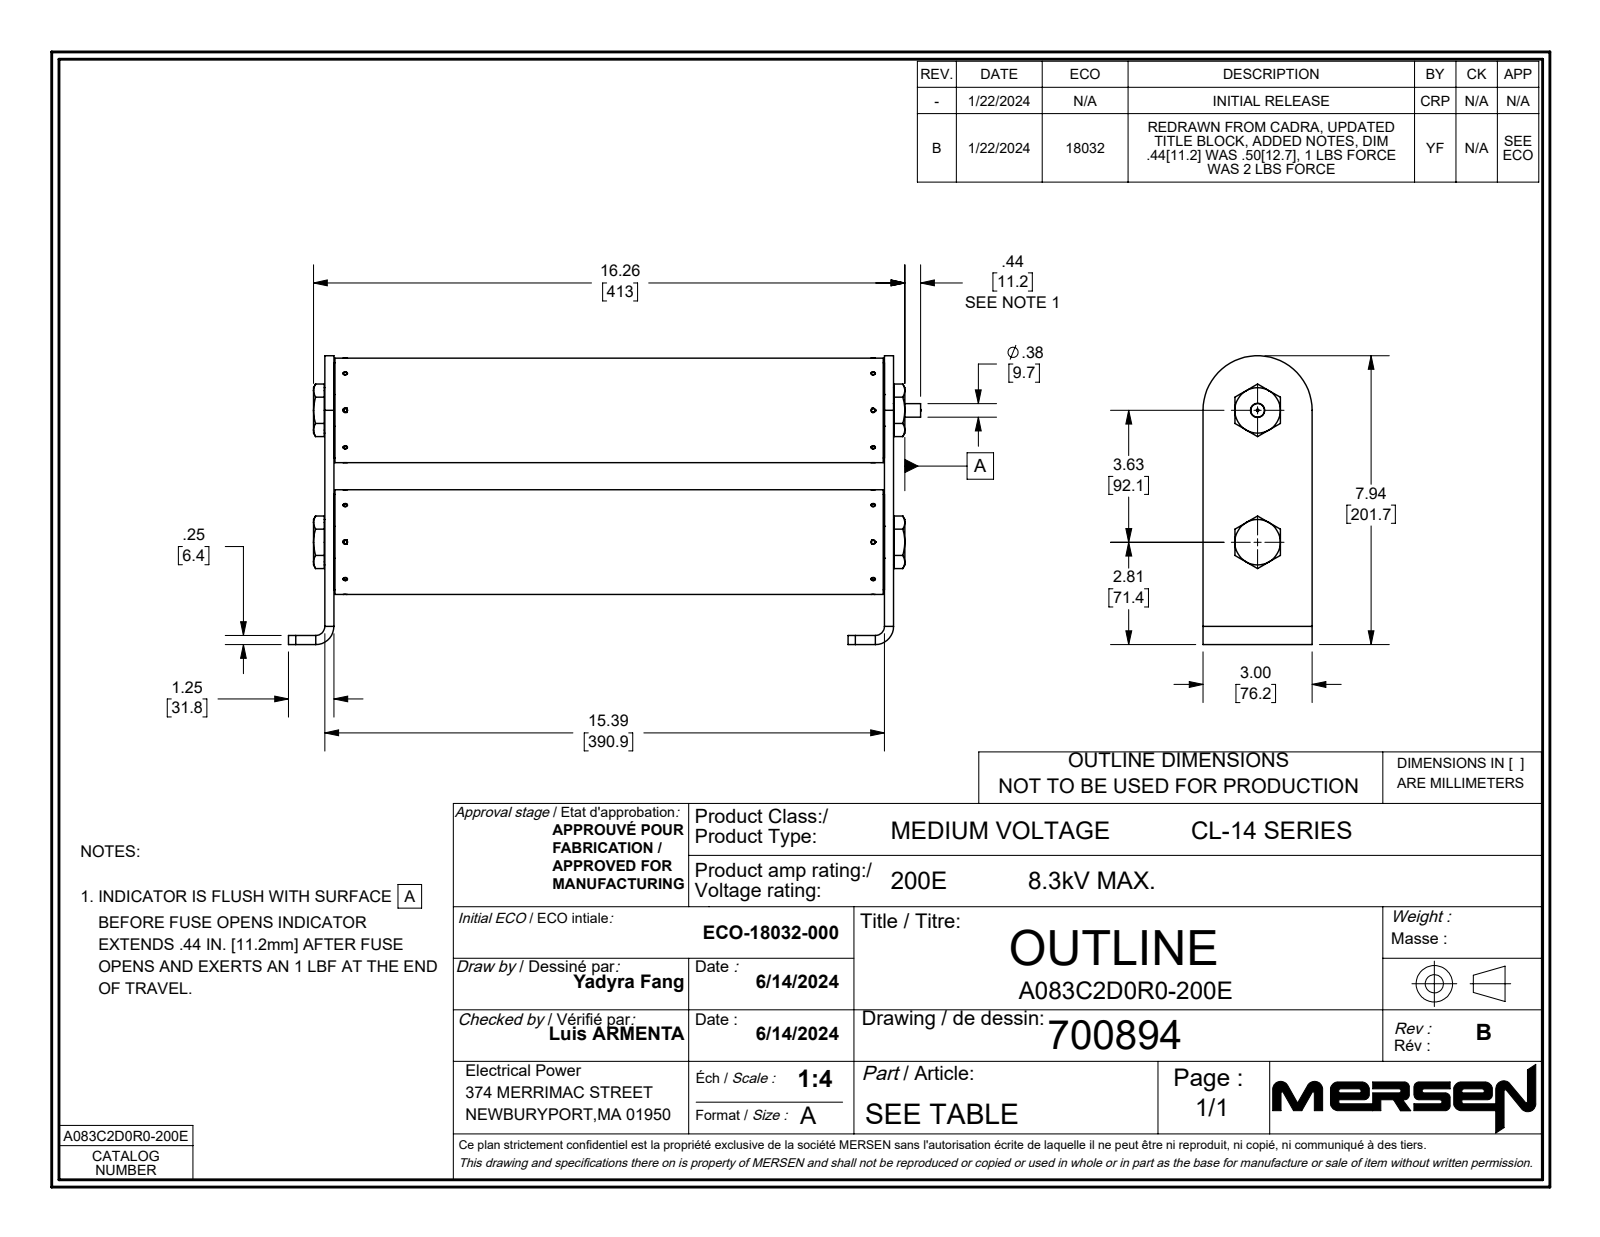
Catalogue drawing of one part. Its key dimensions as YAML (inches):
part_name: "700894"
step_written_by: "SolidWorks 2021 (AUTOMOTIVE_DESIGN)"
units: inches
bodies: {solids: 43, faces: 3685, planar: 925, cylindrical: 1548, other: 1212}
overall_size: [16.95, 7.94, 3]
volume: 48.31
surface_area: 672.1
round_holes:
  - {diameter: 0.125, count: 22}
  - {diameter: 0.906, count: 2}
  - {diameter: 2.625, count: 2}
  - {diameter: 0.02, count: 1}
  - {diameter: 0.063, count: 1}
  - {diameter: 0.146, count: 1}
  - {diameter: 0.189, count: 1}
  - {diameter: 0.391, count: 1}
  - {diameter: 0.465, count: 1}
  - {diameter: 0.512, count: 1}
round_bosses_or_shafts:
  - {diameter: 2.875, count: 2}
  - {diameter: 1.25, count: 2}
  - {diameter: 0.782, count: 2}
  - {diameter: 0.125, count: 2}
  - {diameter: 0.875, count: 1}
  - {diameter: 0.875, count: 1}
  - {diameter: 0.78, count: 1}
  - {diameter: 0.562, count: 1}
partial_cylinders:
  - {radius: 4, count: 120}
  - {radius: 0.2, count: 4}
  - {radius: 0.25, count: 2}
  - {radius: 0.5, count: 2}
  - {radius: 1.5, count: 1}
face_to_face_distances: [0.25, 15.39, 15.64, 15.14, 15.7, 0.31, 0.56, 15.95, 0.591, 15.669]
hole_center_spacings: [14.518, 2.56, 14.742, 3.62, 14.963, 3.625]
